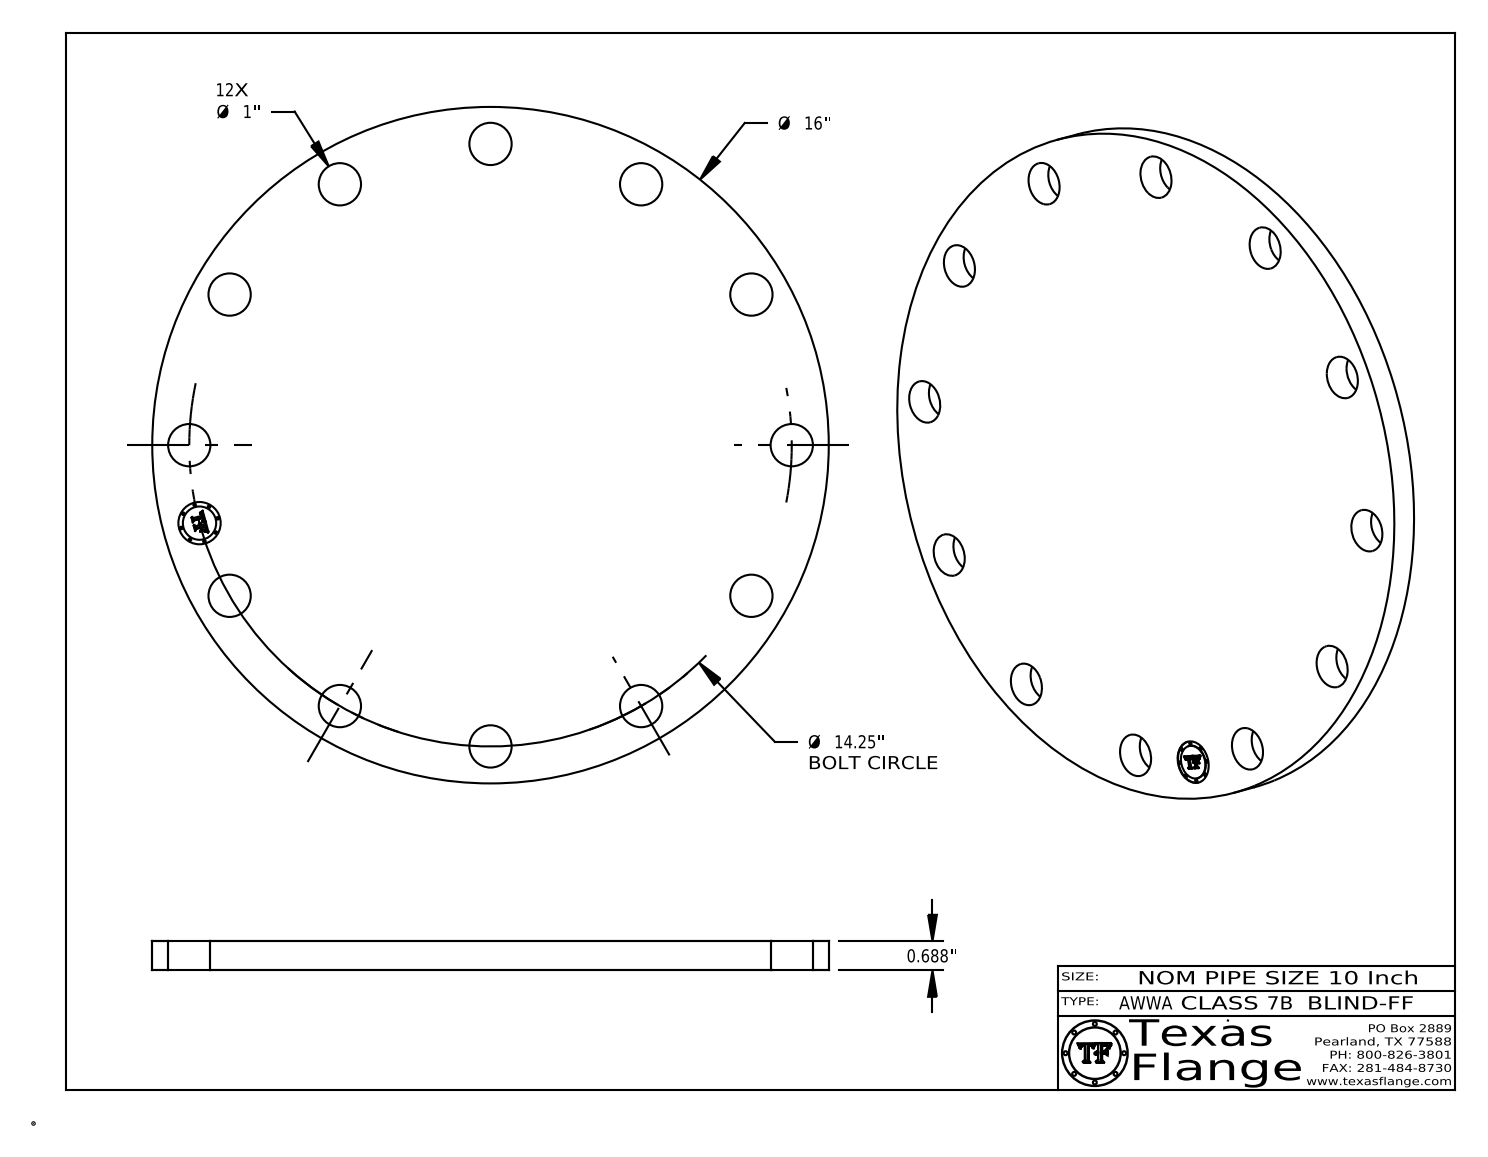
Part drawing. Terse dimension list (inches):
name: AWWA Class 7B-BLIND-FF
written by: CATIA V5 STEP AP214 (AUTOMOTIVE_DESIGN)
unit: in
bodies: 1 solid, 413 faces (367 planar, 46 cylindrical, 0 other)
size: 16 × 16 × 0.688
volume: 131.8 in³; area: 444 in²
holes: 13× ⌀1
bosses: 8× ⌀0.061, 1× ⌀16, 1× ⌀0.788
face distances: 0.688, 0.673, 0.015, 0.298, 0.292, 0.019, 0.054, 0.194, 0.248, 0.044
hole spacings: 3.688, 7.125, 10.076, 12.341, 13.765, 14.25, 11.306, 13.165
